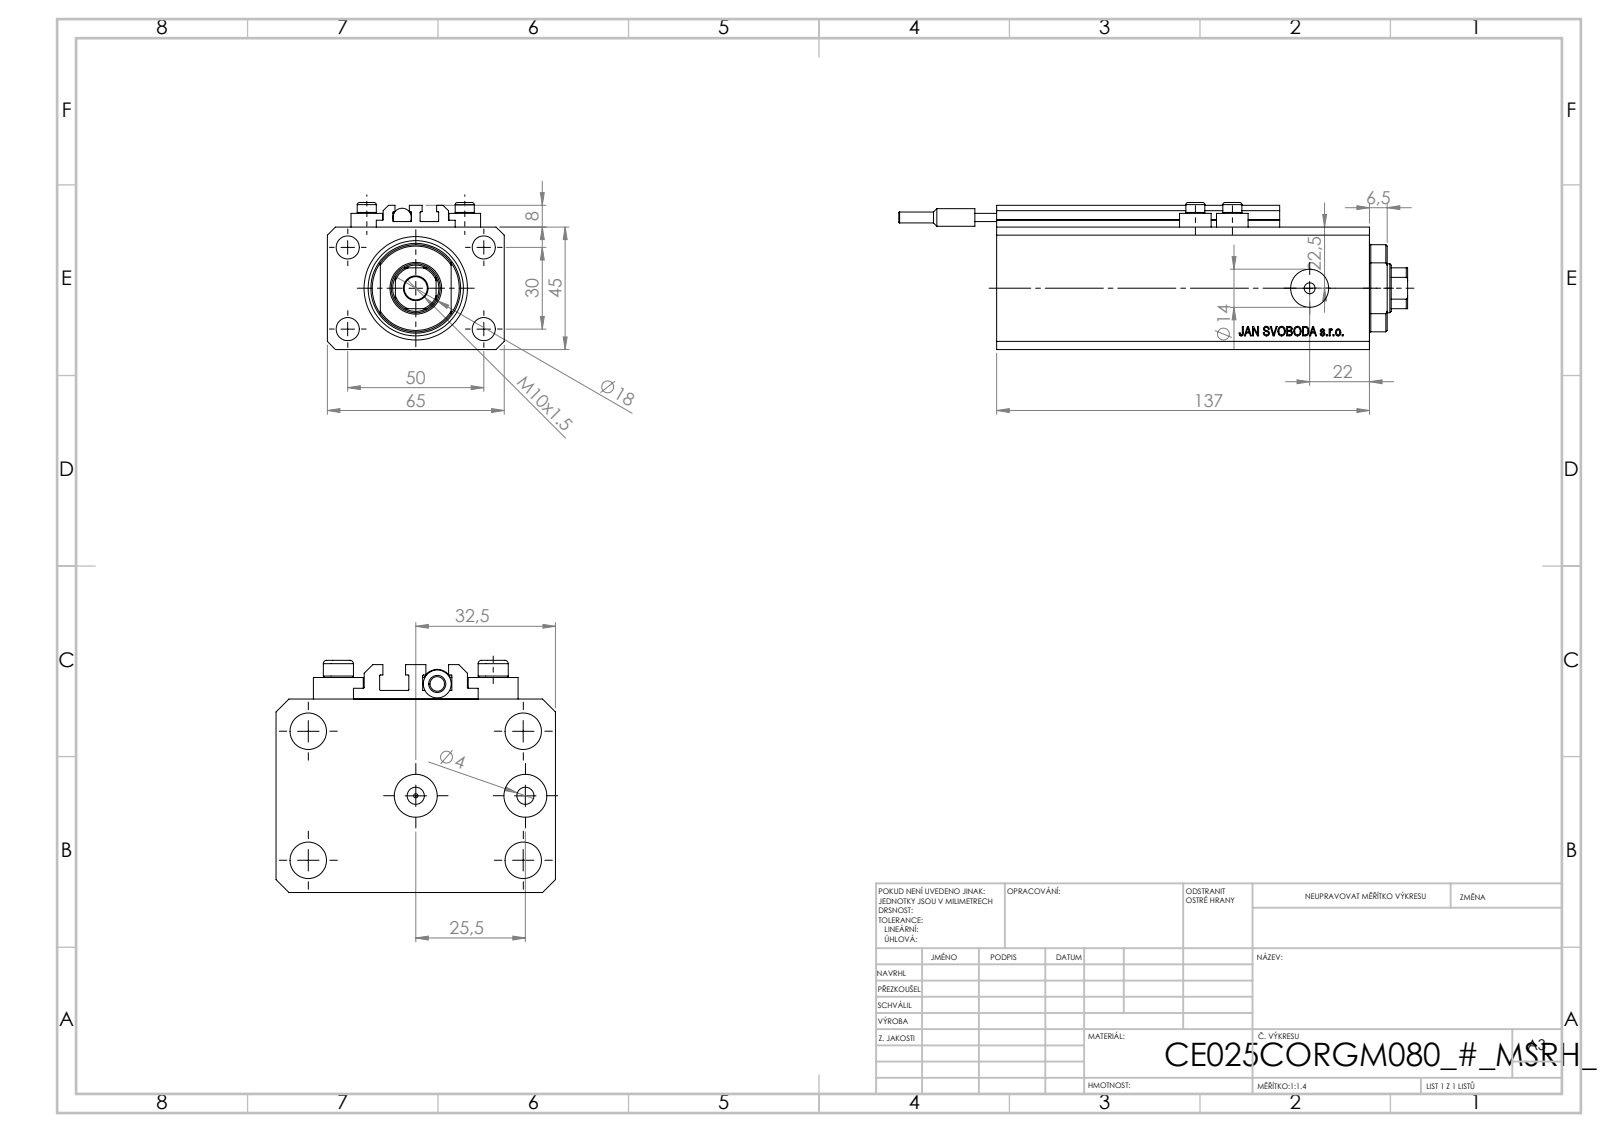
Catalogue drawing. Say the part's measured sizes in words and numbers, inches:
The part is named "V250CE_C_VCP; ALLEN BOLT V250CE; V250CE_VC_C; V250CE_C_Body (+1 more)". Its 3-D file was written by "SolidWorks 2019 (CONFIG_CONTROL_DESIGN)". It is 9 solids with 1064 faces: 520 planar, 94 cylindrical and 450 other. Overall it measures 7.362 by 2.559 by 2.126 inches. Its volume is 22.42 cubic inches and its surface area 143.3 square inches. Round holes: 8 of diameter 0.157, 5 of diameter 0.335, 2 of diameter 0.394, 2 of diameter 0.551, 1 of diameter 0.049, 1 of diameter 0.709, 1 of diameter 0.984, 1 of diameter 1.496. Round bosses or shafts: 4 of diameter 0.457, 4 of diameter 0.276, 1 of diameter 0.268, 1 of diameter 0.256, 1 of diameter 0.157. Partial cylindrical surfaces (rounded edges, fillets, slot ends): 10 of radius 0.008, 1 of radius 0.335, 1 of radius 0.63. The main face-to-face distances are 1.772, 2.559, 1.85, 0.551, 5.394, 4.843, 0.098, 0.079, 0.394, 0.807. The hole center spacings are 1.148, 0.535, 0.591, 1.181, 1.417, 1.515, 1.969, 2.074.
